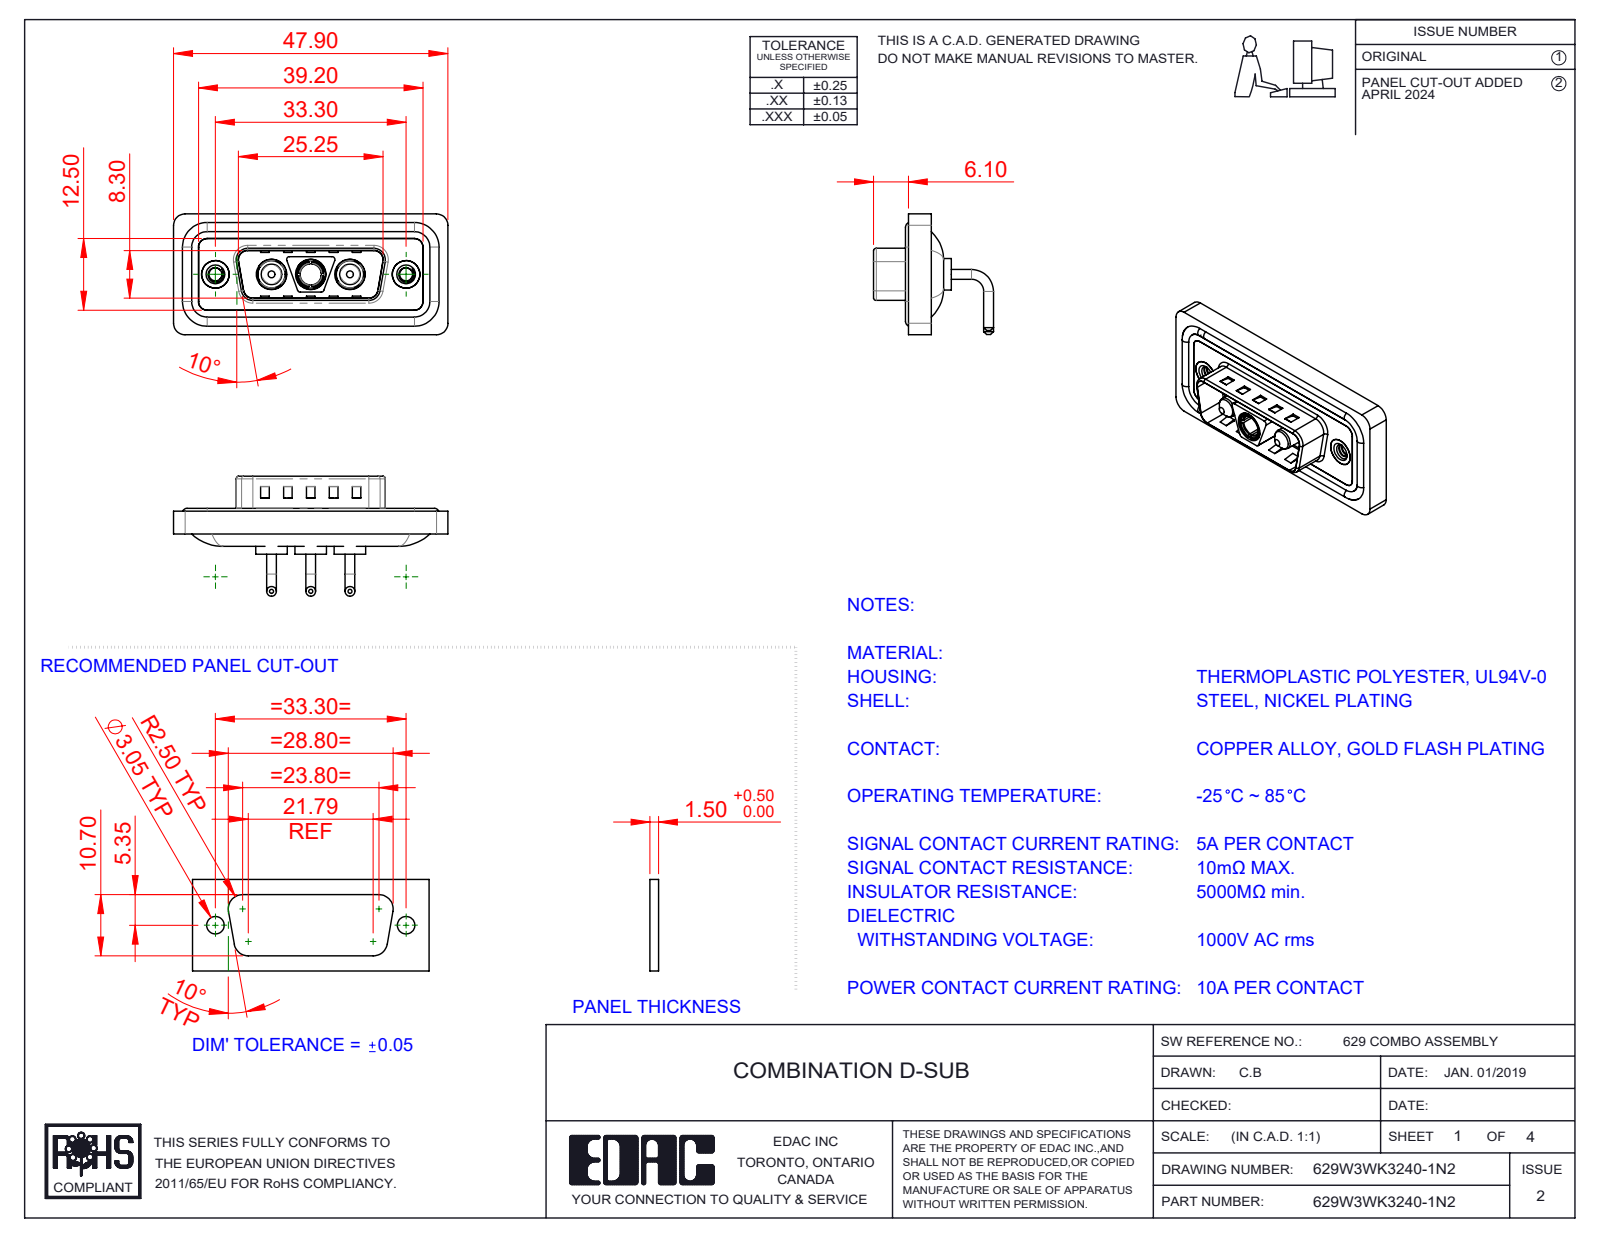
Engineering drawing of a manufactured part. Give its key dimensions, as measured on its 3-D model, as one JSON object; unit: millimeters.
{"part_name": "629W3WK3140-1N2; Power Socket_10A RA; 629Combo Threaded Rivet_2; 629Combo Waterproof Housing_15 Contacts (+4 more)", "step_written_by": "SolidWorks 2023 (CONFIG_CONTROL_DESIGN)", "units": "millimeters", "bodies": {"solids": 13, "faces": 621, "planar": 231, "cylindrical": 256, "other": 134}, "overall_size": [47.9, 21.1, 20.95], "volume_mm3": 5719, "surface_area_mm2": 9261, "round_holes": [[4.85, 3], [5.3, 3], [2.26, 2], [4, 2], [4.8, 2], [5, 2], [3.7, 1]], "round_bosses_or_shafts": [[1.7, 6], [1.6, 4], [5.5, 3], [5.2, 3], [4.75, 3], [3.75, 3], [4.9, 2], [3.6, 2]], "partial_cylinders_radius": [[2, 20], [1.5, 18], [0.5, 12], [1.6, 8], [0.25, 4], [0.6, 4], [0.65, 4], [0.9, 4]], "face_to_face_distances": [0.4, 2.9, 0.8, 1.1, 2.1, 1.6, 3.1, 2.5, 4.5, 1.5], "hole_center_spacings": [6.85, 9.8, 16.65, 23.5, 13.7, 33.3]}
